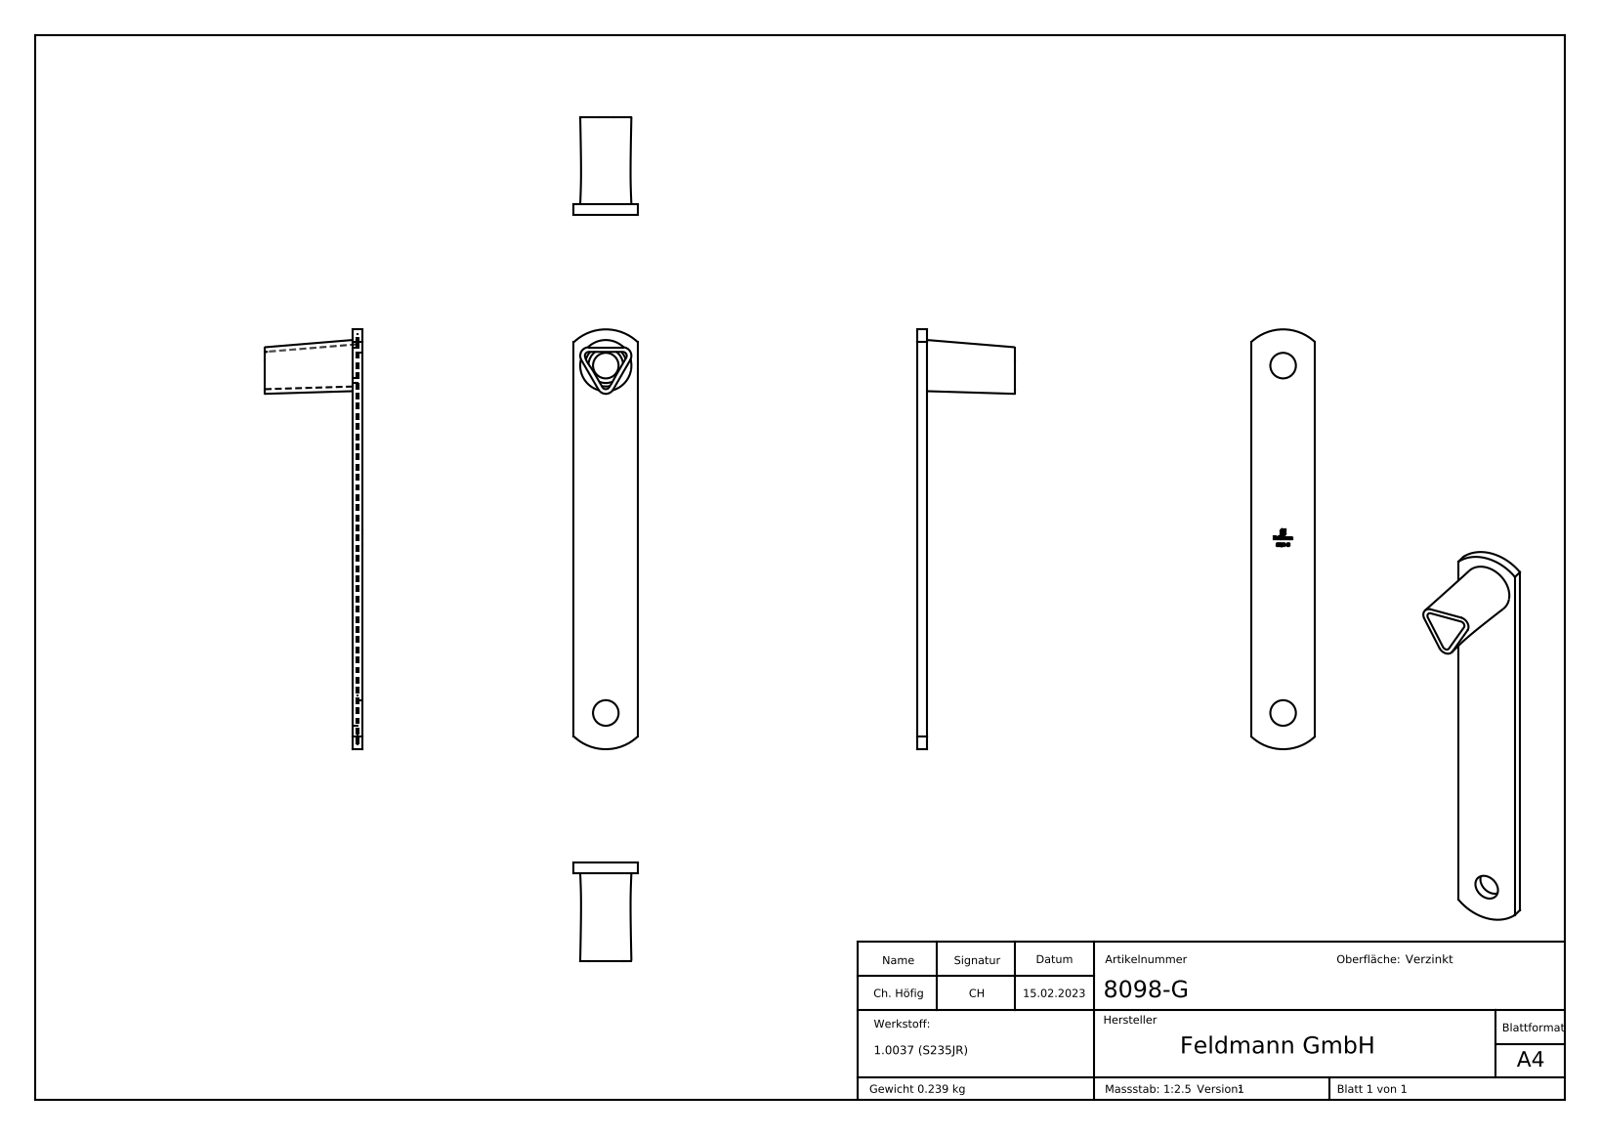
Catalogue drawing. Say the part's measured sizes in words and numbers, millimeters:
The part is named "8098-G". Its 3-D file was written by "SolidWorks 2018 (CONFIG_CONTROL_DESIGN)". It is 1 solid with 260 faces: 121 planar, 8 cylindrical and 131 other. Overall it measures 197 by 46 by 30 millimeters. Its volume is 29 083 cubic millimeters and its surface area 28 434 square millimeters. Round holes: 2 of diameter 12. Round bosses or shafts: 2 of diameter 16.35. Partial cylindrical surfaces (rounded edges, fillets, slot ends): 2 of radius 19.57, 2 of radius 21.75. The main face-to-face distances are 2.17, 2.83, 5, 0.66, 30, 27.83, 46, 43.83, 43.17, 41. The hole center spacings are 163.
